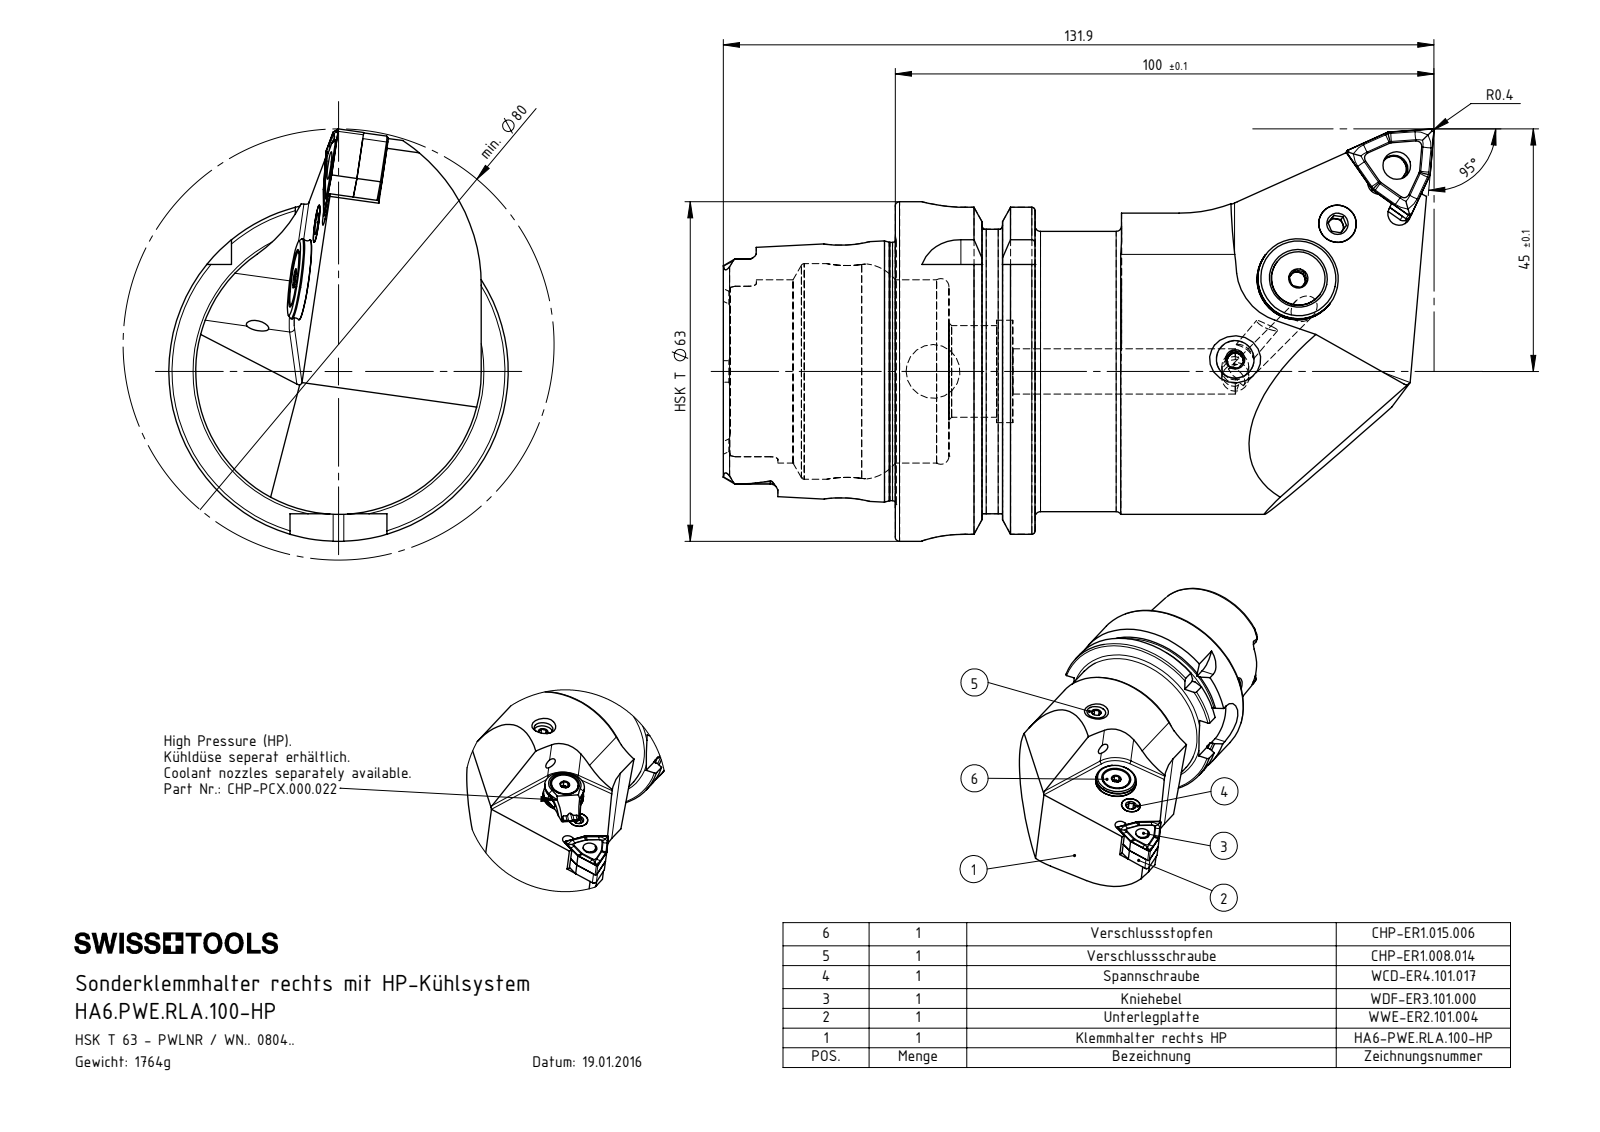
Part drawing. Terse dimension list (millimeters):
name: CHP-ER1.008.014_A; DIN 3771 - 13x1; WWE-ER2.101.004_A; WCD-ER4.101.017_A (+8 more)
written by: SolidWorks 2017 (AUTOMOTIVE_DESIGN)
unit: mm
bodies: 10 solids, 269 faces (101 planar, 57 cylindrical, 111 other)
size: 71.5 × 58.13 × 53
volume: 4 102 mm³; area: 7 423 mm²
holes: 1× ⌀1.2, 1× ⌀2.5, 1× ⌀3, 1× ⌀5.16, 1× ⌀5.2, 1× ⌀6.7, 1× ⌀7.8
bosses: 2× ⌀8, 1× ⌀15, 1× ⌀13.4, 1× ⌀10, 1× ⌀7.9, 1× ⌀6.4, 1× ⌀5.5, 1× ⌀5
rounds: 3× R0.4, 3× R1, 1× R2.35, 1× R2.8, 1× R3.1, 1× R3.2, 1× R26.5
face distances: 4.76, 4.72, 5.8, 10.52, 10.56, 4.7, 16.92, 11.12, 6.4, 6.36
hole spacings: 24.65, 24.66, 4.47, 4.48, 28.49, 28.5
